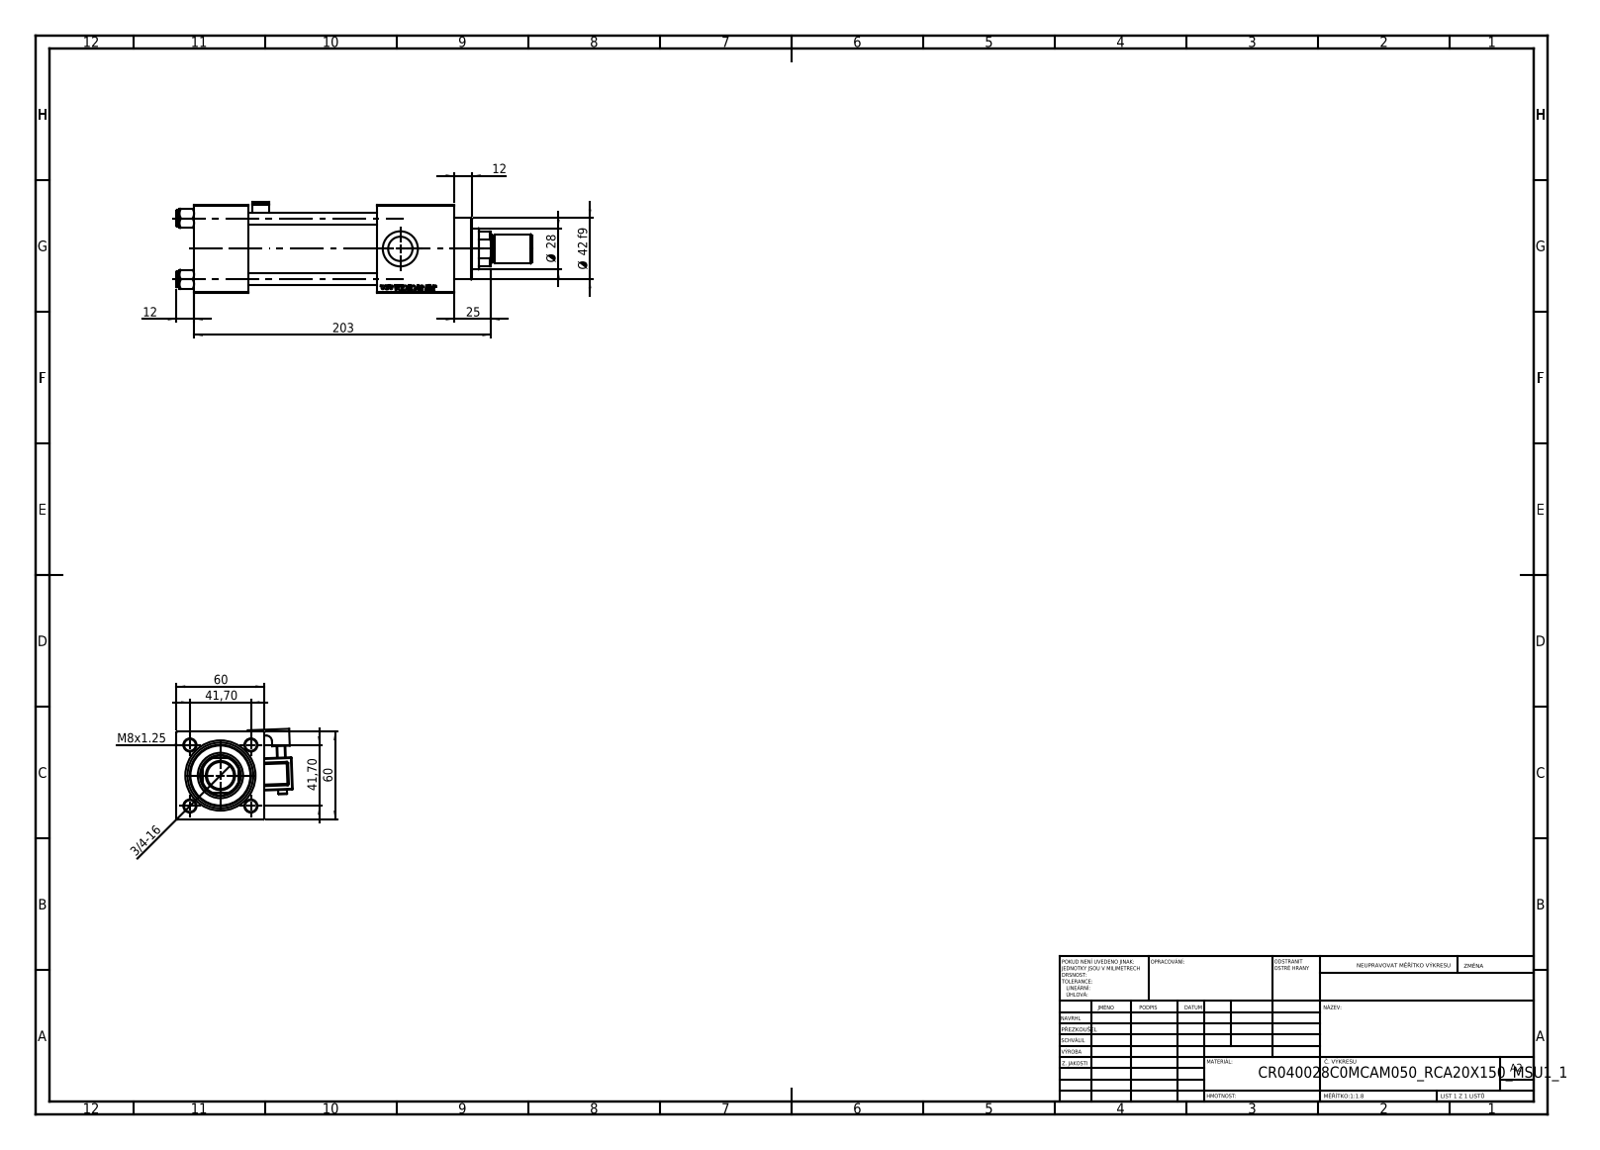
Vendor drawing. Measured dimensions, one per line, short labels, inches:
name: ROD_END_AH; V215CR_C_Body; NUT_M5_C; V215CR_VCP_C (+3 more)
written by: SolidWorks 2019 (CONFIG_CONTROL_DESIGN)
unit: in
bodies: 13 solids, 1240 faces (559 planar, 121 cylindrical, 560 other)
size: 9.567 × 3.127 × 2.437
volume: 29.89 in³; area: 207.2 in²
holes: 4× ⌀0.315, 2× ⌀0.276, 2× ⌀0.656, 2× ⌀0.945, 1× ⌀0.728, 1× ⌀1.102, 1× ⌀1.22, 1× ⌀1.575, 1× ⌀1.772
bosses: 4× ⌀0.433, 1× ⌀1.811, 1× ⌀1.654, 1× ⌀0.787, 1× ⌀0.709, 1× ⌀0.236
rounds: 24× R0.02, 1× R0.039, 1× R0.098, 1× R0.157, 1× R0.531
face distances: 2.362, 1.457, 4.921, 3.465, 2.087, 5.878, 4.421, 0.957, 7.008, 5.551
hole spacings: 1.161, 1.642, 2.322
